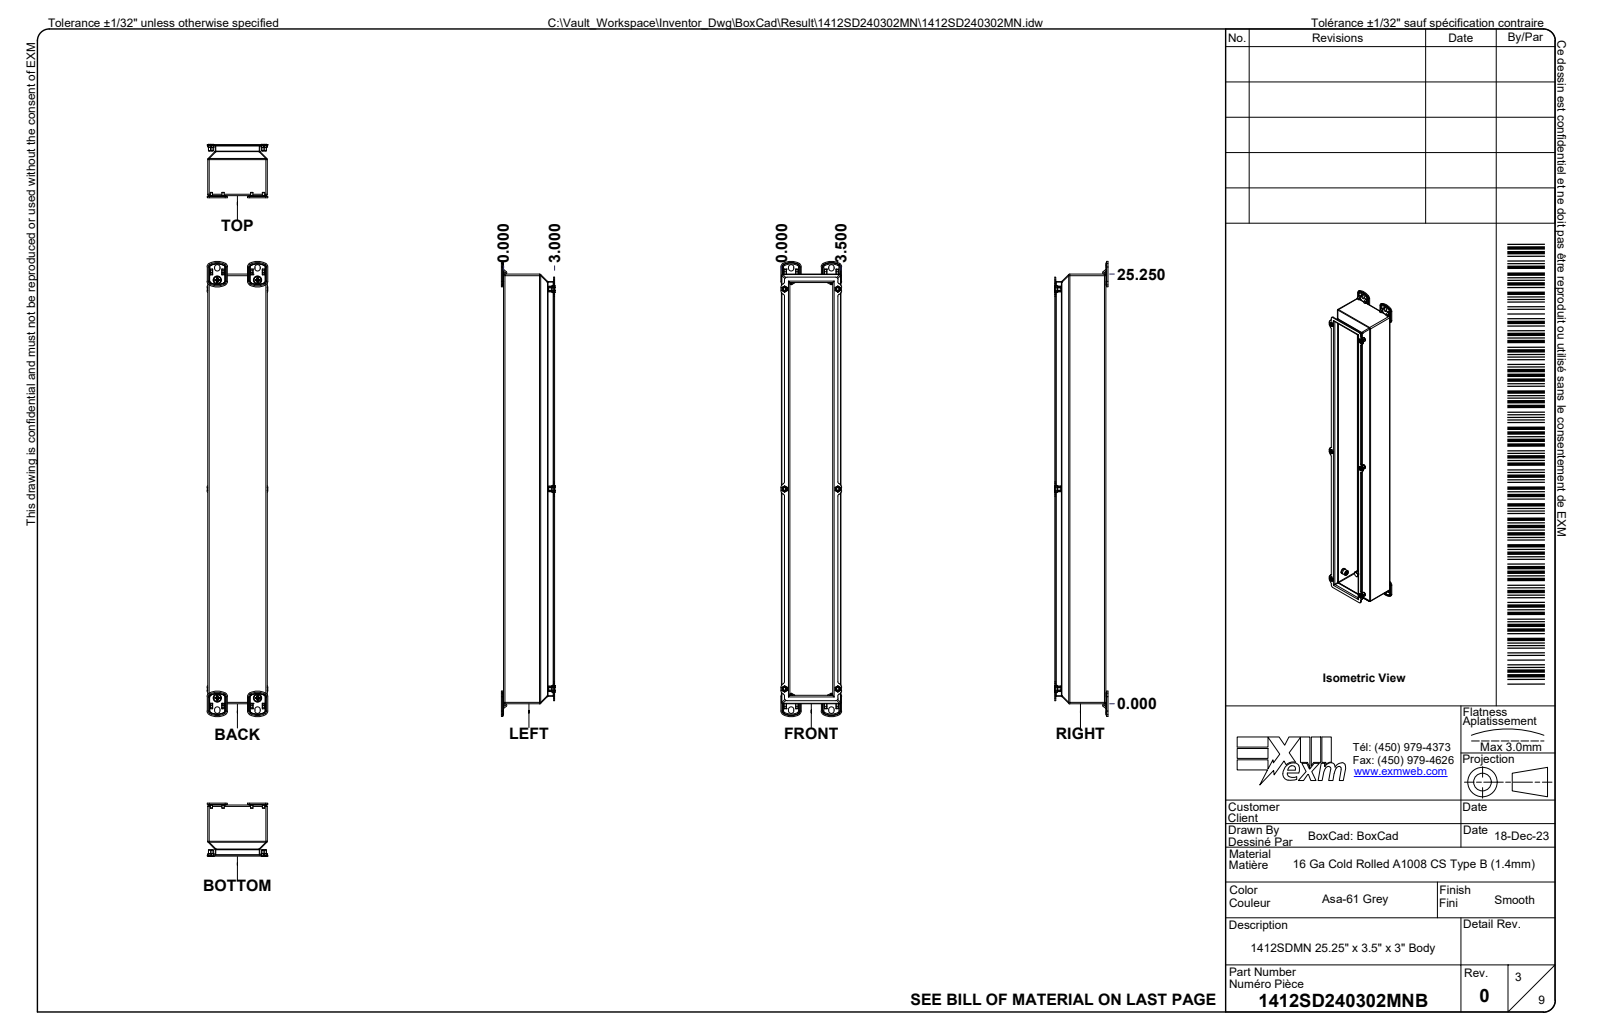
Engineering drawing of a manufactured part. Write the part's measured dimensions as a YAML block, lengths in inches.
part_name: "1412SD240302MN; 1412SD240302MNB; 1412SD240302MNB-P; RIVET_NUT_M5_FH_OE (+8 more)"
step_written_by: "Autodesk Inventor 2024 (AUTOMOTIVE_DESIGN)"
units: inches
bodies: {solids: 35, faces: 3722, planar: 1026, cylindrical: 1268, other: 1428}
overall_size: [26.746, 3.736, 3.441]
volume: 24.41
surface_area: 886.7
round_holes:
  - {diameter: 0.875, count: 10}
  - {diameter: 0.157, count: 6}
  - {diameter: 0.198, count: 6}
  - {diameter: 0.277, count: 6}
  - {diameter: 0.197, count: 4}
  - {diameter: 0.03, count: 2}
  - {diameter: 0.201, count: 2}
  - {diameter: 0.23, count: 2}
  - {diameter: 0.24, count: 2}
round_bosses_or_shafts:
  - {diameter: 0.591, count: 6}
  - {diameter: 0.277, count: 6}
  - {diameter: 0.193, count: 6}
  - {diameter: 0.138, count: 6}
  - {diameter: 0.5, count: 4}
  - {diameter: 0.232, count: 4}
  - {diameter: 0.394, count: 2}
  - {diameter: 0.035, count: 2}
partial_cylinders:
  - {radius: 0.008, count: 292}
  - {radius: 0.004, count: 100}
  - {radius: 0.01, count: 60}
  - {radius: 0.039, count: 41}
  - {radius: 0.012, count: 36}
  - {radius: 0.031, count: 28}
  - {radius: 0.047, count: 28}
  - {radius: 0.236, count: 28}
face_to_face_distances: [0.053, 0.053, 3.447, 3.092, 3.039, 3.145, 3.092, 0.118, 3.5, 3.394]
hole_center_spacings: [2.25, 4.5, 6.75, 9, 11.25, 0.652, 1.928, 2.804]
